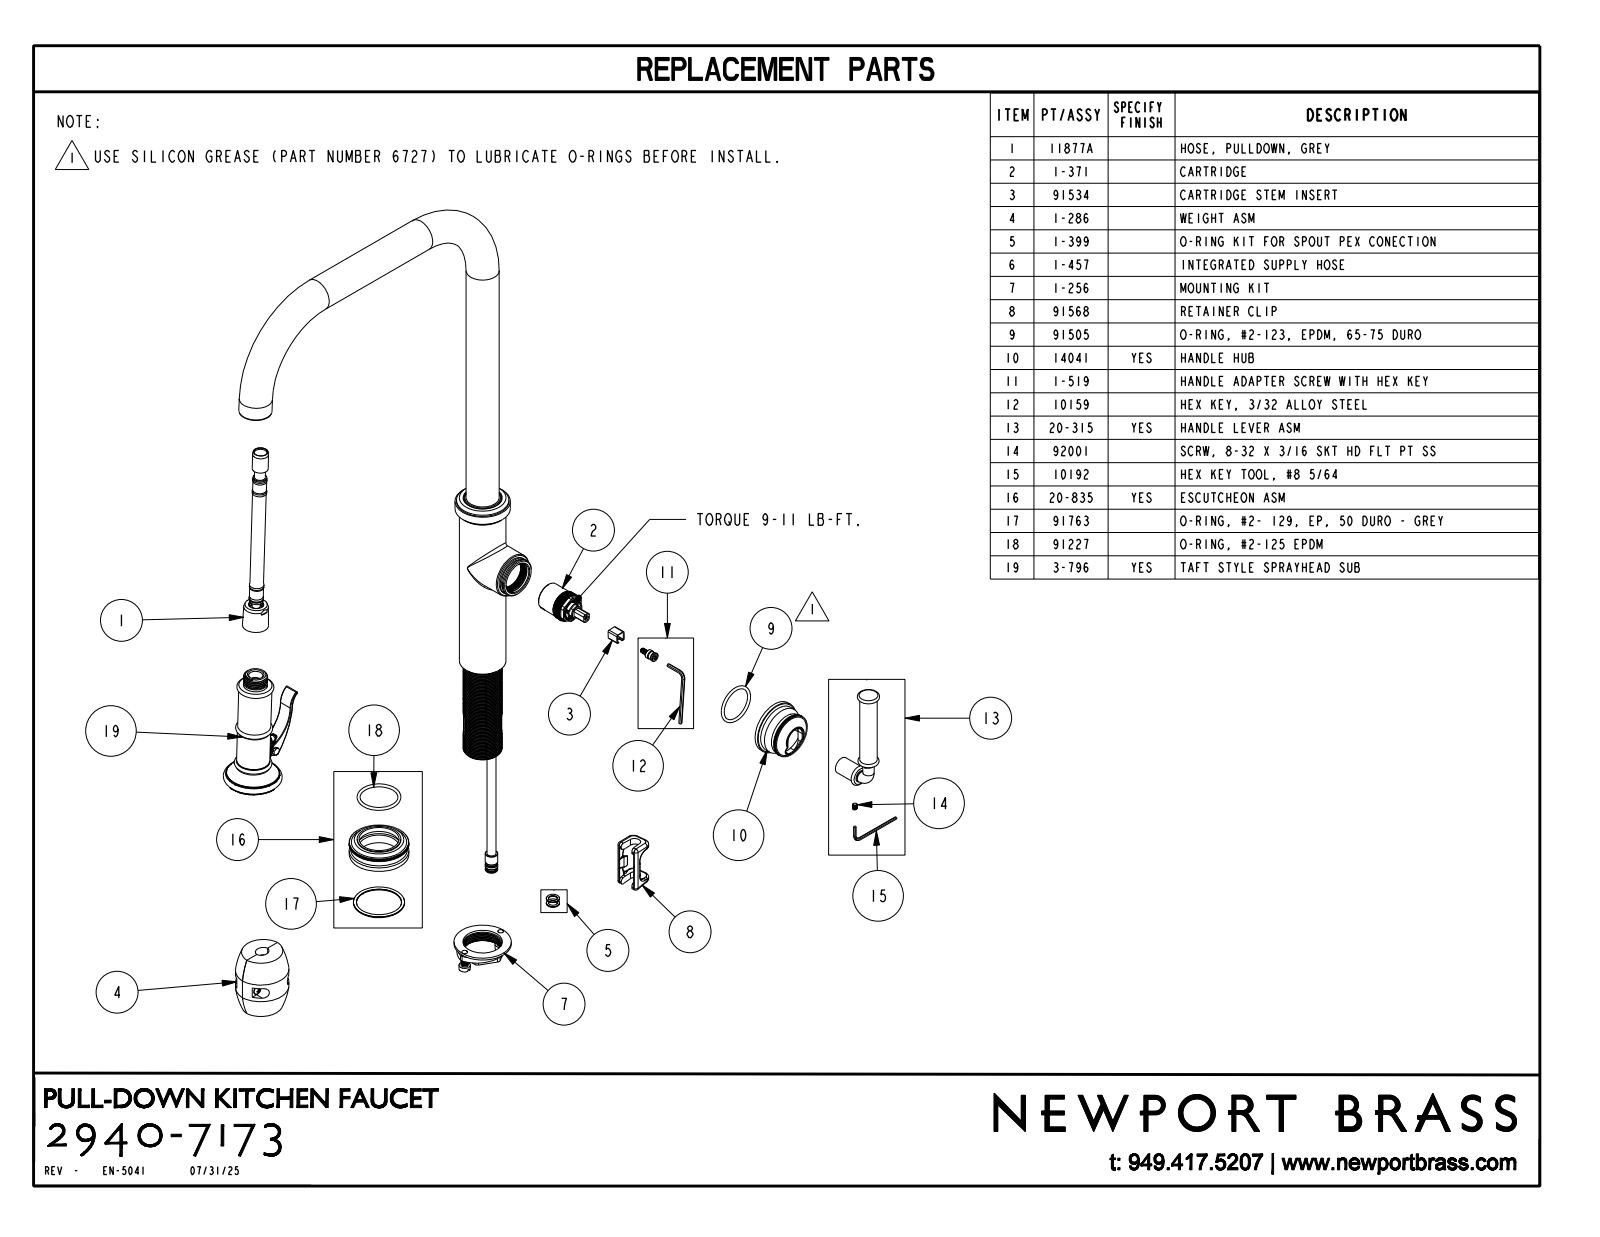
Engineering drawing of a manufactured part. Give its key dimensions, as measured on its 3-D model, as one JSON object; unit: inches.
{"part_name": "2940-7173", "step_written_by": "CREO PARAMETRIC BY PTC INC, 2025093 (CONFIG_CONTROL_DESIGN)", "units": "inches", "bodies": {"solids": 3, "faces": 1935, "planar": 939, "cylindrical": 581, "other": 415}, "overall_size": [20.6, 13.213, 4.804], "volume_in3": 50.35, "surface_area_in2": 181.9, "round_holes": [[0.228, 1], [0.41, 1]], "round_bosses_or_shafts": [[0.102, 18], [0.39, 2], [2.05, 1], [1.95, 1], [1.9, 1], [1.874, 1], [1.8, 1], [1.694, 1]], "partial_cylinders_radius": [[0.02, 18], [0.03, 15], [0.065, 12], [0.025, 7], [0.06, 5], [0.045, 4], [0.353, 2], [0.04, 1]], "face_to_face_distances": [7.45, 3.933, 3.959, 0.025, 7.485, 0.035, 0.1, 0.015, 6.41, 7.47]}
